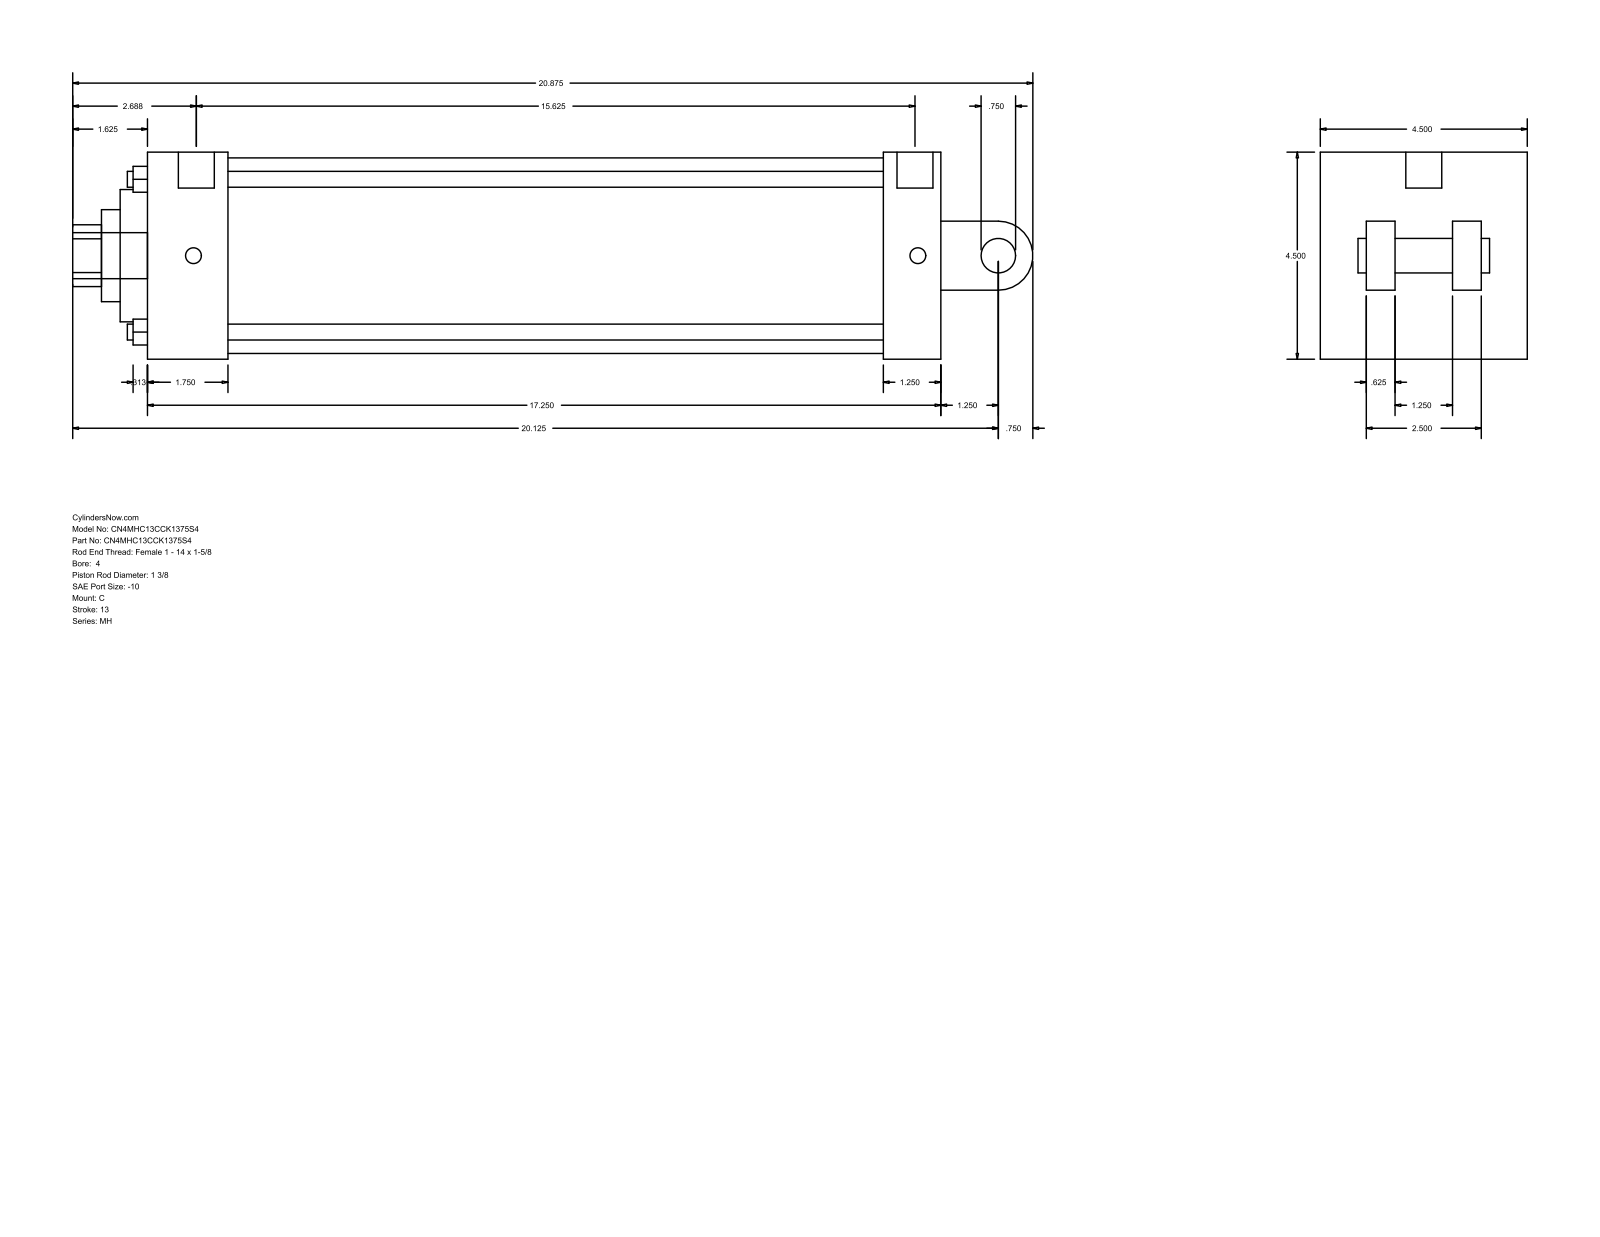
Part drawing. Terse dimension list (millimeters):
name: MH_C__0400_1.375
written by: GSSL Pune (CONFIG_CONTROL_DESIGN)
unit: mm
bodies: 0 solids, 101 faces (71 planar, 30 cylindrical, 0 other)
size: 530.23 × 114.3 × 114.3
holes: 4× ⌀8.76, 2× ⌀8.73, 1× ⌀19.84, 1× ⌀34.92, 1× ⌀50.8, 1× ⌀73.03, 1× ⌀107.95
bosses: 2× ⌀8.73, 1× ⌀25.4, 1× ⌀19.84, 1× ⌀19.05
rounds: 1× R17.06, 1× R19.05
face distances: 114.3, 438.16, 44.45, 406.41, 361.96, 393.71, 31.75, 73.03, 41.27, 38.1
hole spacings: 59.62, 84.32, 119.25, 1.59
